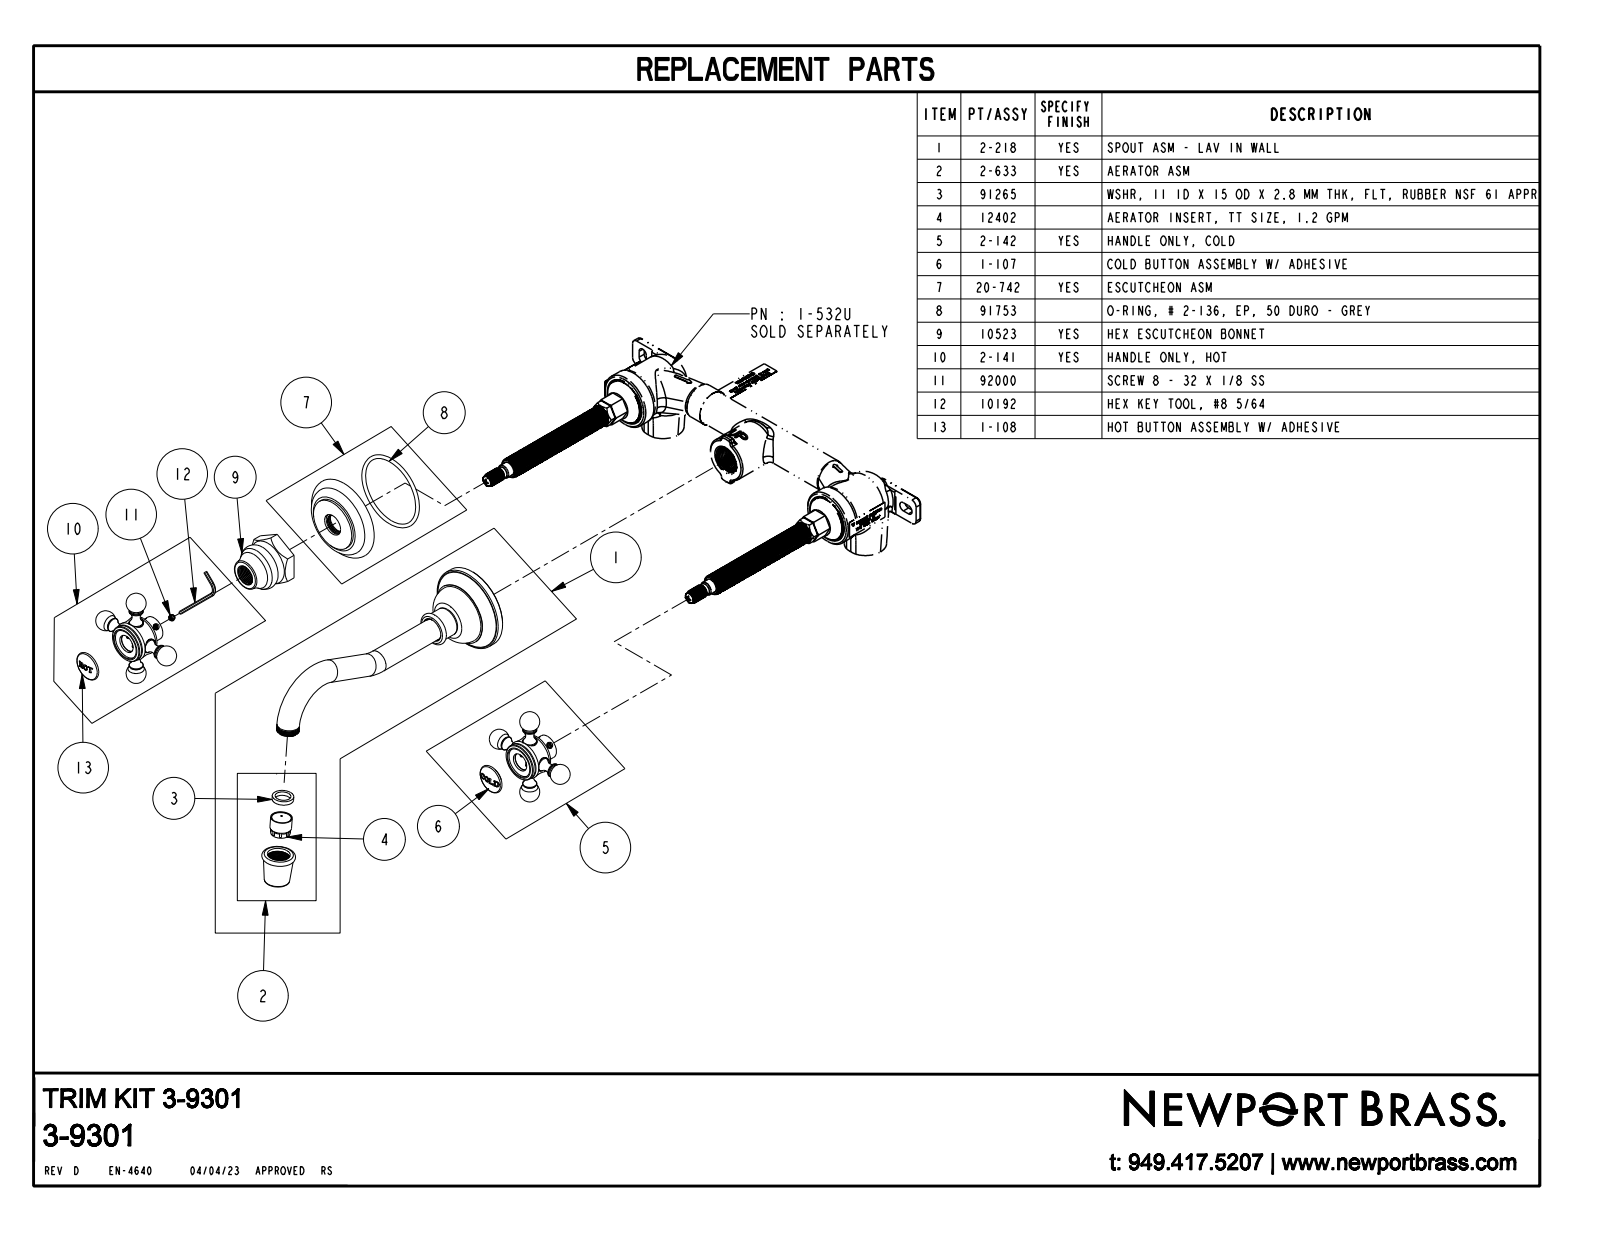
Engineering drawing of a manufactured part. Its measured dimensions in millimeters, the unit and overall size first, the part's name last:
Units: millimetres
Overall size (bounding box): 274 × 194.6 × 74
Round holes (diameter × count): ⌀10.4 ×4
Round bosses / shafts (diameter × count): ⌀10 ×4, ⌀37.6 ×2, ⌀26.8 ×2, ⌀17.4 ×2, ⌀15.9 ×2, ⌀59.9 ×1, ⌀44.8 ×1, ⌀20.7 ×1
Partial cylindrical surfaces — rounded edges, fillets, slot ends (radius × count): R0.2 ×7, R0.6 ×7, R0.8 ×5, R1.2 ×3, R0.5 ×2, R0.9 ×2, R1 ×2, R1.4 ×1
Main face-to-face distances: 33.4, 33.4, 9.5, 24.4, 14.9, 11.1, 1.6, 13.3, 13.2, 3.7
Hole centre spacings: 200
Volume: 221 900 mm³ · Surface area: 50 260 mm²
Bodies: 3 solids, 435 faces (125 planar, 94 cylindrical, 216 other)
Part name (STEP PRODUCT): 3-9301_SW0001
STEP written by: CREO PARAMETRIC BY PTC INC, 2018400 (AUTOMOTIVE_DESIGN)
